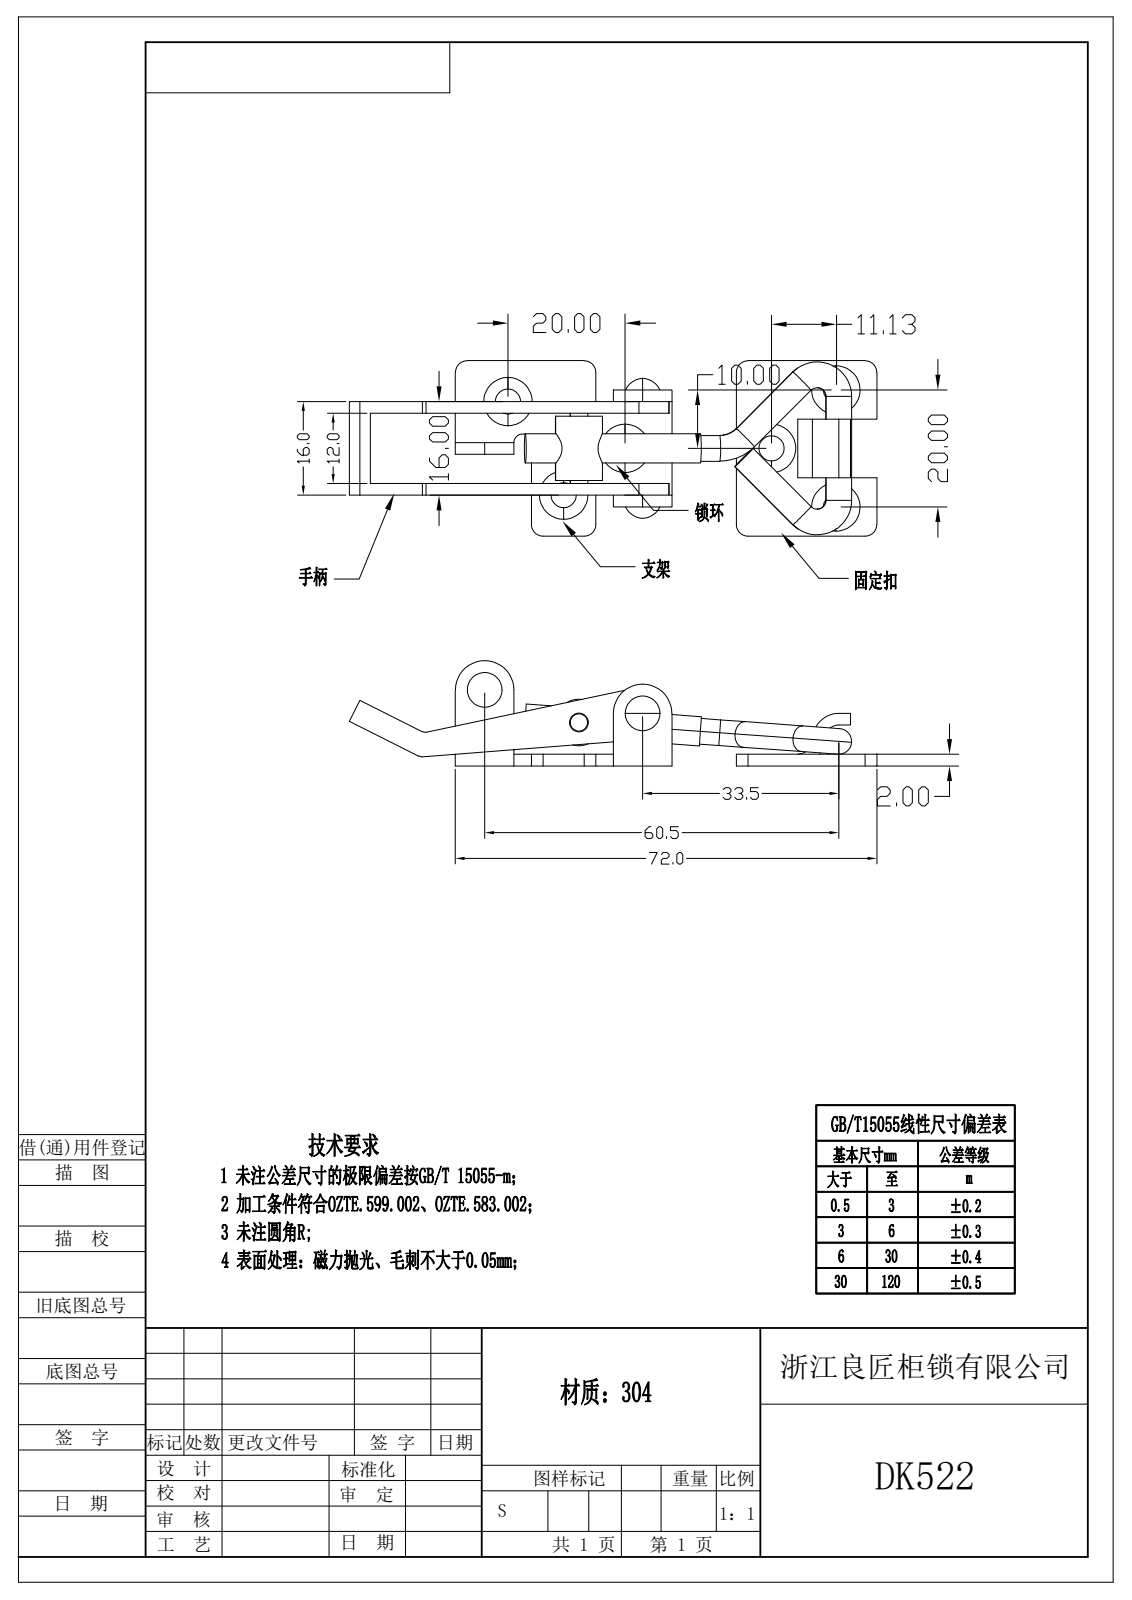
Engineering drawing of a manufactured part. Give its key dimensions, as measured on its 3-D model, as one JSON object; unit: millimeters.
{"step_written_by": "Rhino 8.5 (CONFIG_CONTROL_DESIGN)", "units": "millimeters", "bodies": {"solids": 8, "faces": 253, "planar": 77, "cylindrical": 143, "other": 33}, "overall_size": [89.79, 34.5, 18], "volume_mm3": 4724, "surface_area_mm2": 8728, "round_holes": [[4.3, 4], [3, 2], [6, 1]], "round_bosses_or_shafts": [[4.4, 4], [3.5, 4], [8, 1], [4, 1], [3.2, 1]], "partial_cylinders_radius": [[2, 10], [1, 6], [4, 4], [0.5, 3], [1.5, 2], [2.5, 2], [4.5, 2], [5, 2]], "face_to_face_distances": [2, 14, 16, 7, 9, 5, 4.5, 4, 12, 11], "hole_center_spacings": [14.87, 11, 17.05, 20, 27.29, 45.31, 56.54, 57.77]}
